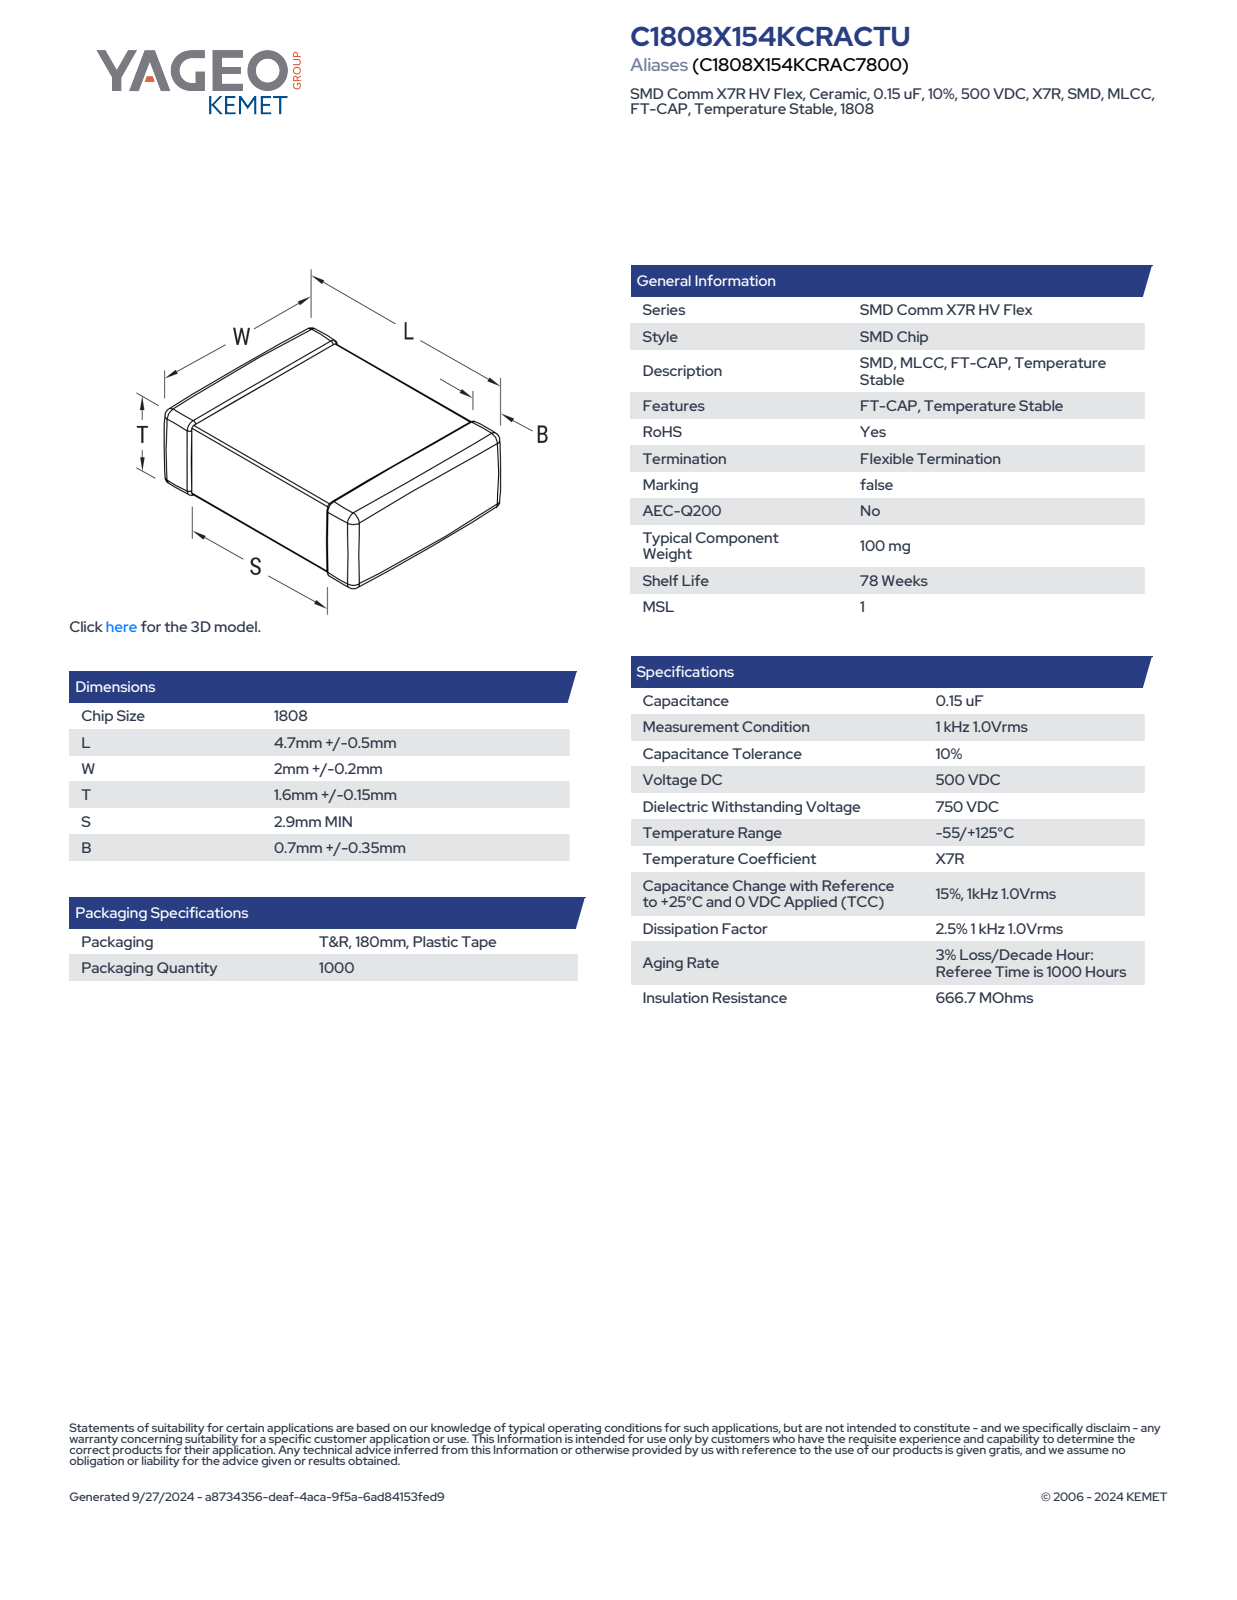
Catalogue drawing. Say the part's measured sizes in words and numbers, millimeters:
The part is named "CCS_CCSTDNOS_1808_L5.2W2.2T1.75B1.05". Its 3-D file was written by "SolidWorks 2014 (AUTOMOTIVE_DESIGN)". It is 4 solids with 121 faces: 71 planar, 34 cylindrical and 16 other. Overall it measures 5.2 by 2.2 by 1.75 millimeters. Its volume is 19 cubic millimeters and its surface area 48 square millimeters. The main face-to-face distances are 1.7, 2.15, 1.65, 2.1, 1.75, 5.2, 2.2, 1.71, 1.66, 0.89.
